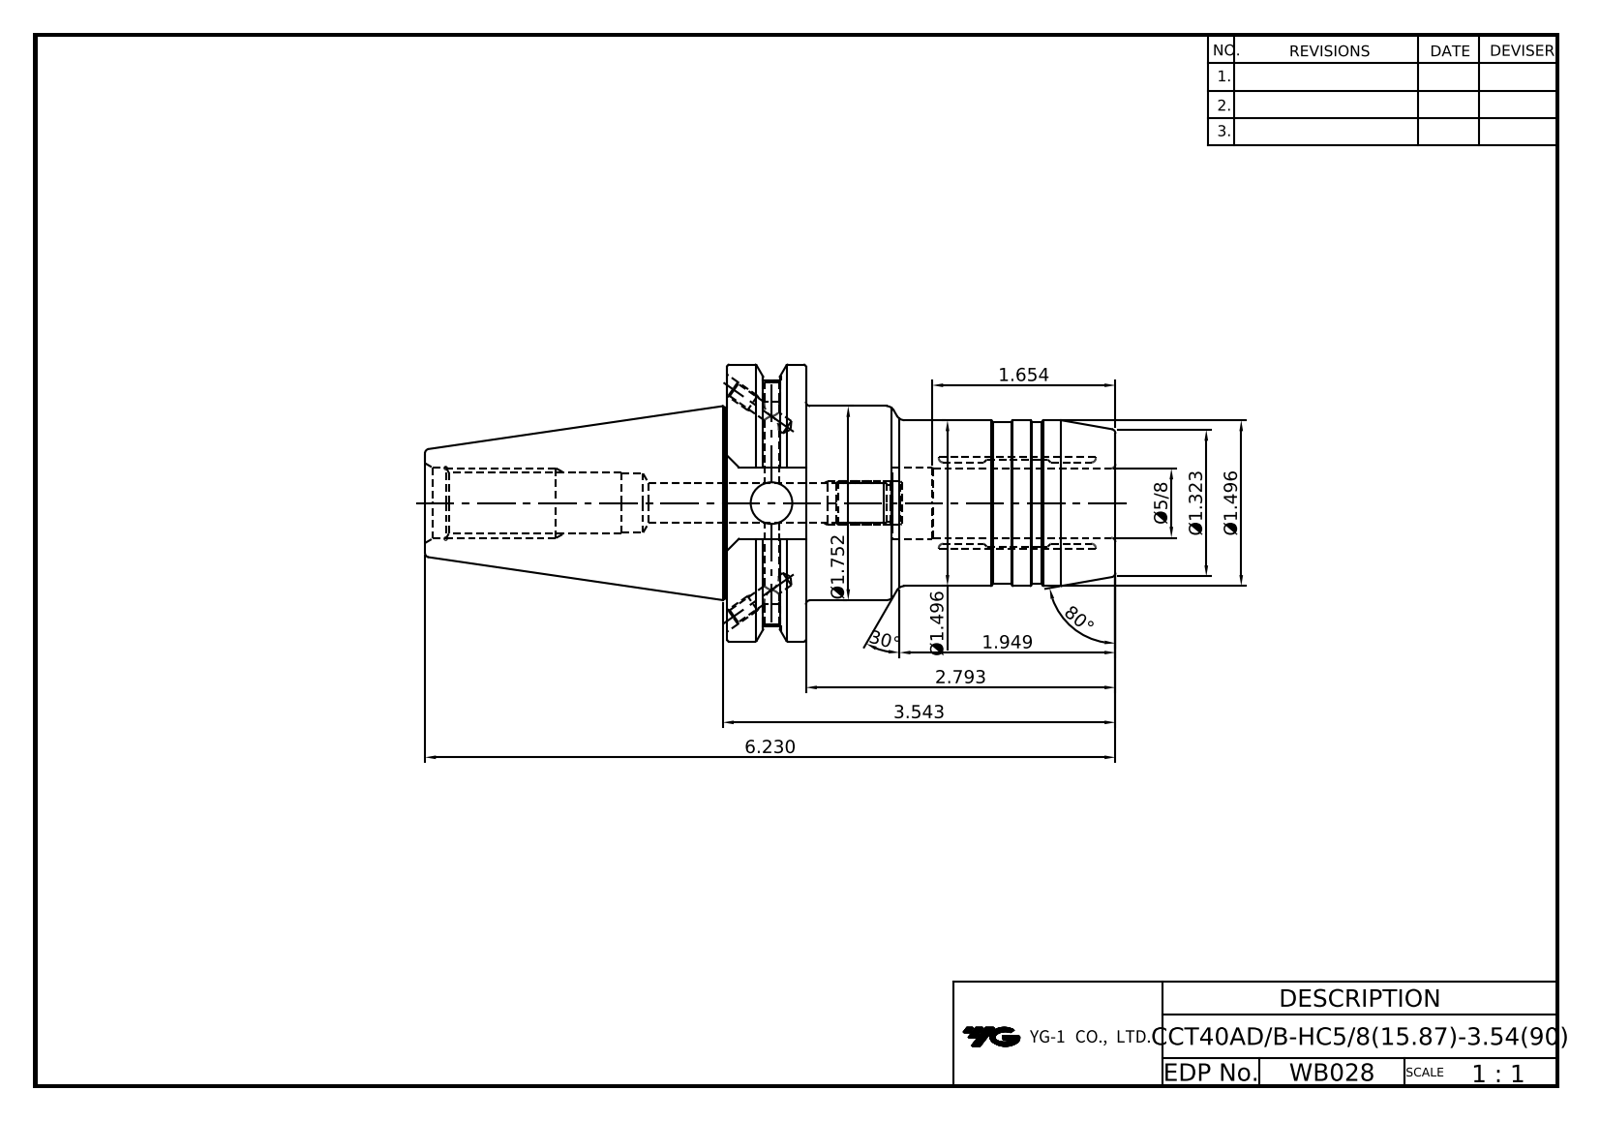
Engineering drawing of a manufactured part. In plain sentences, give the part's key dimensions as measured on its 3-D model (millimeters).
The part is named "LO-CCT40ADB-HC15.875-90". Its 3-D file was written by "Autodesk Inventor 2022 (AUTOMOTIVE_DESIGN)". It is 1 solid with 106 faces: 34 planar, 34 cylindrical and 38 other. Overall it measures 158.25 by 63.5 by 61.09 millimeters. Its volume is 182 086 cubic millimeters and its surface area 32 059 square millimeters. Round holes: 4 of diameter 3.24, 2 of diameter 4, 2 of diameter 4.2, 1 of diameter 8.92, 1 of diameter 9.53, 1 of diameter 13, 1 of diameter 13.39, 1 of diameter 15.88, 1 of diameter 16.3, 1 of diameter 16.4. Round bosses or shafts: 1 of diameter 63.5, 1 of diameter 44.5, 1 of diameter 43.8, 1 of diameter 38, 1 of diameter 37. Partial cylindrical surfaces (rounded edges, fillets, slot ends): 1 of radius 28.15. The main face-to-face distances are 18.05, 89, 70.95, 47.6, 16.38, 38, 19.95, 51, 69.25, 87.3.
